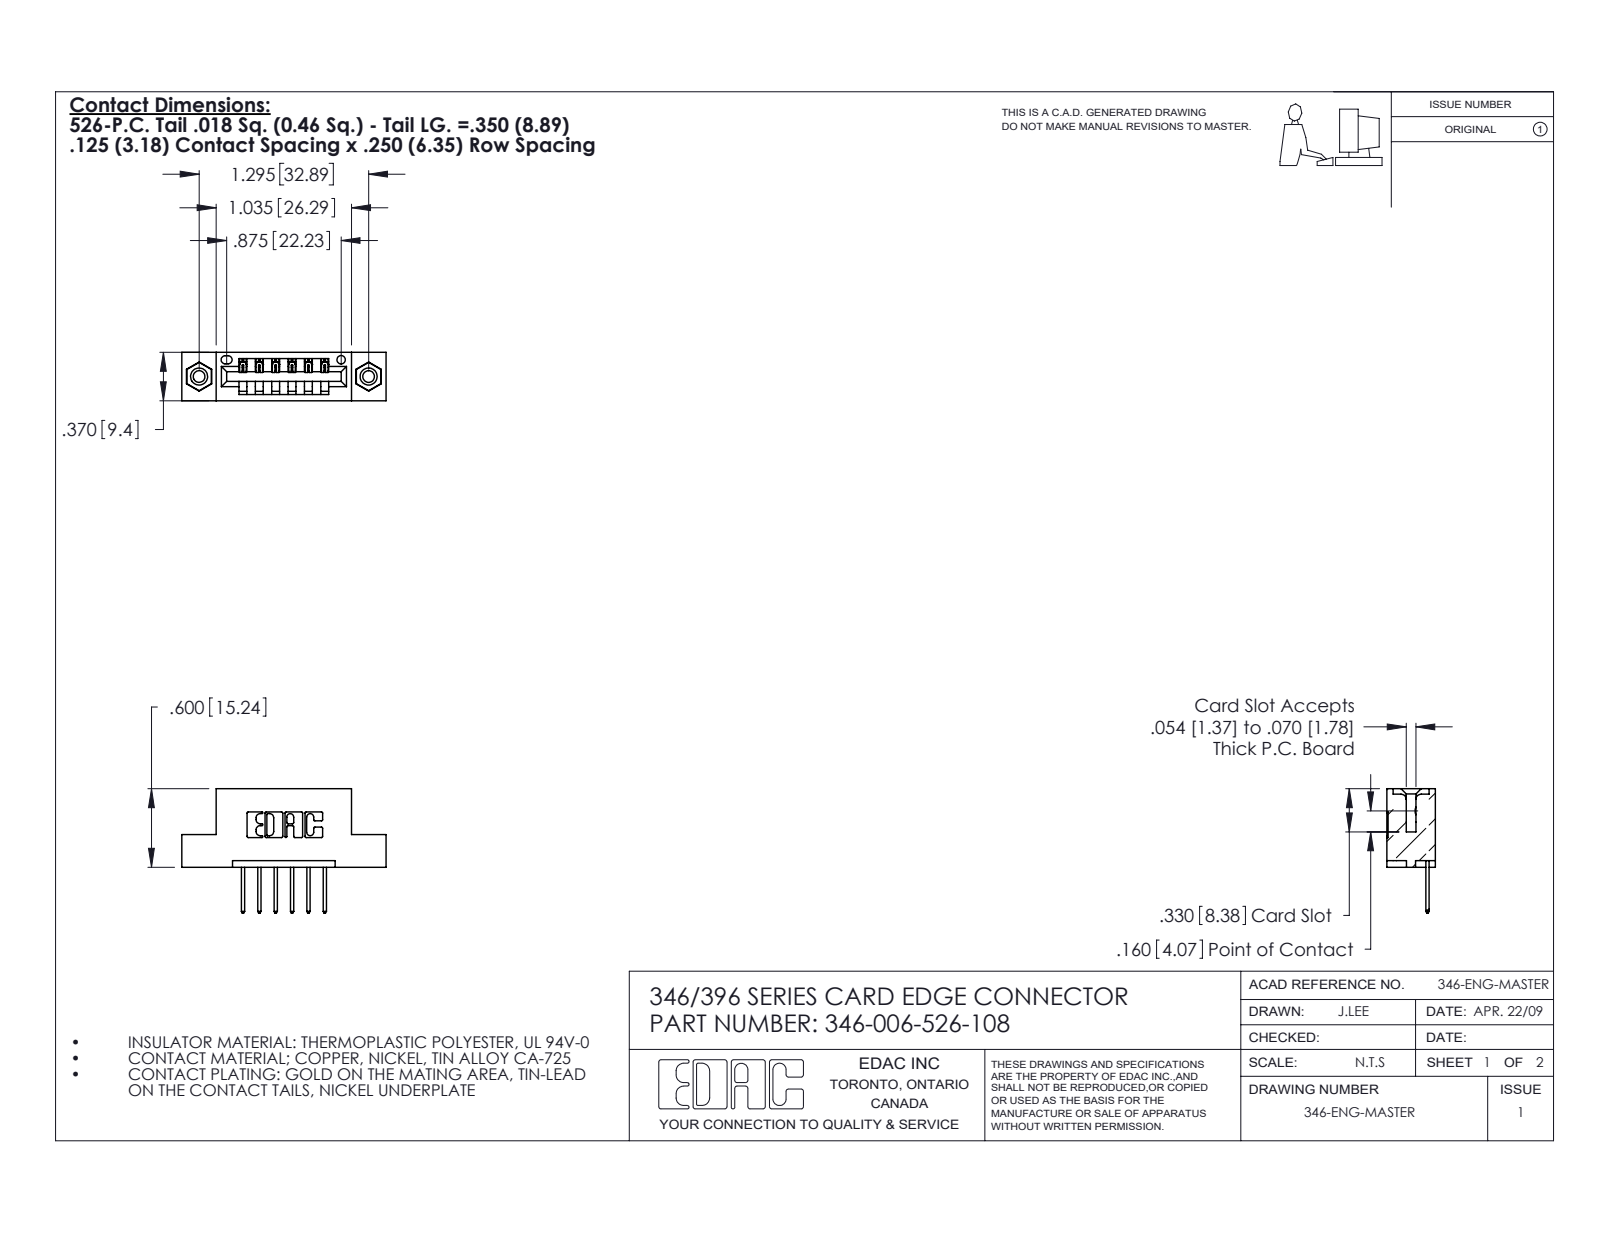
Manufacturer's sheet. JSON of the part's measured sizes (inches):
{"part_name": "346 Part_Flush Mounting Lugs - 0.156 Dia-TI; 345-292-001_345-293-126; 346-006-526-108; 345-250-001_345-250-003-102", "step_written_by": "SolidWorks 2020 (CONFIG_CONTROL_DESIGN)", "units": "inches", "bodies": {"solids": 9, "faces": 530, "planar": 348, "cylindrical": 166, "other": 16}, "overall_size": [1.56, 0.95, 0.37], "volume_in3": 0.216, "surface_area_in2": 6.268, "round_holes": [[0.089, 2], [0.125, 2], [0.156, 2], [0.064, 1]], "round_bosses_or_shafts": [[0.155, 2]], "partial_cylinders_radius": [[0.01, 22], [0.006, 12], [0.01, 12], [0.007, 6], [0.031, 6], [0.026, 3], [0.031, 2], [0.04, 2]], "face_to_face_distances": [0.25, 0.37, 0.048, 0.322, 0.148, 0.222, 0.1, 0.174, 0.072, 0.298], "hole_center_spacings": [0.246, 1.092, 1.295]}
